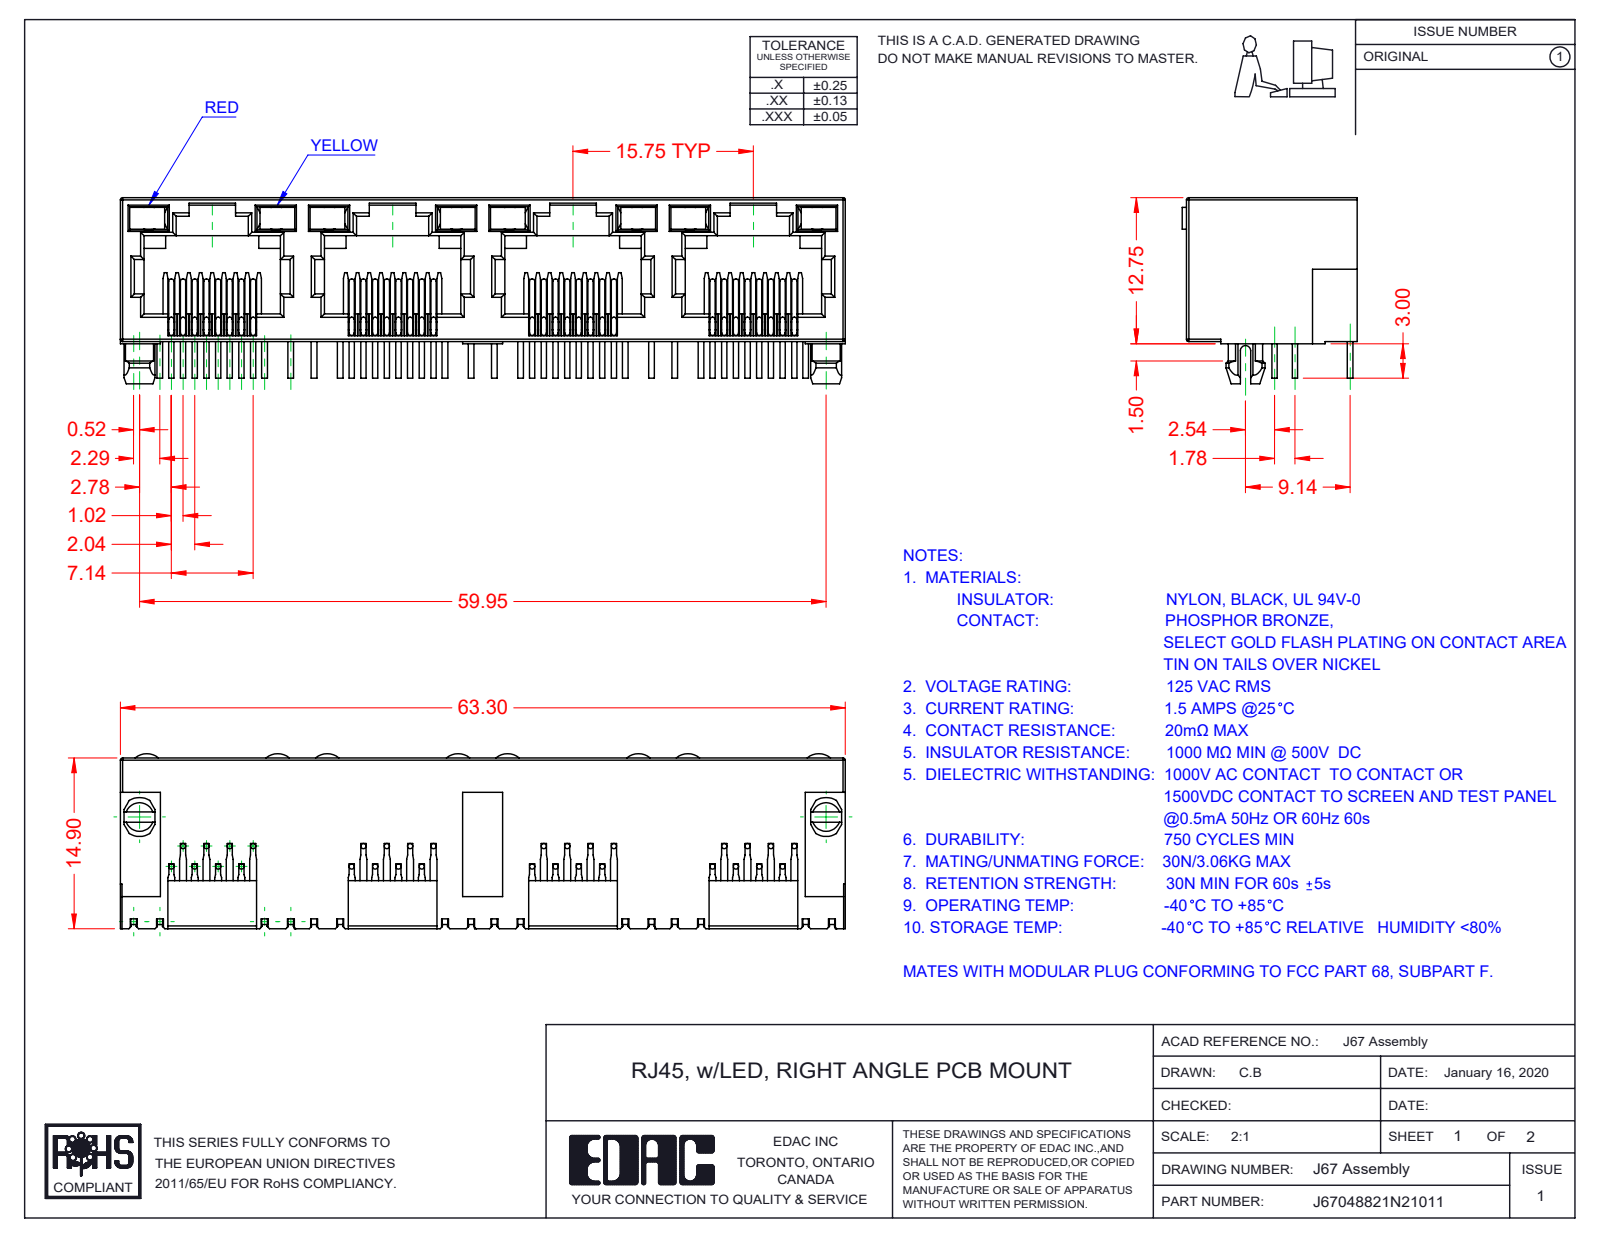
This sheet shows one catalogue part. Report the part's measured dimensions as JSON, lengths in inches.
{"part_name": "67 LED RH_1-Yellow; 67 Contacts; J67048822N21011; 67 LED LH_2-Red (+1 more)", "step_written_by": "SolidWorks 2016 (CONFIG_CONTROL_DESIGN)", "units": "inches", "bodies": {"solids": 41, "faces": 2465, "planar": 1781, "cylindrical": 476, "other": 208}, "overall_size": [2.492, 0.64, 0.602], "volume_in3": 0.315, "surface_area_in2": 17.94, "round_bosses_or_shafts": [[0.018, 96]], "partial_cylinders_radius": [[0.008, 66], [0.012, 29], [0.018, 9], [0.061, 8], [0.059, 2], [0.067, 2], [0.014, 1], [0.039, 1]], "face_to_face_distances": [0.02, 0.494, 0.074, 0.035, 0.394, 0.62, 0.039, 0.055, 0.433, 0.468]}
